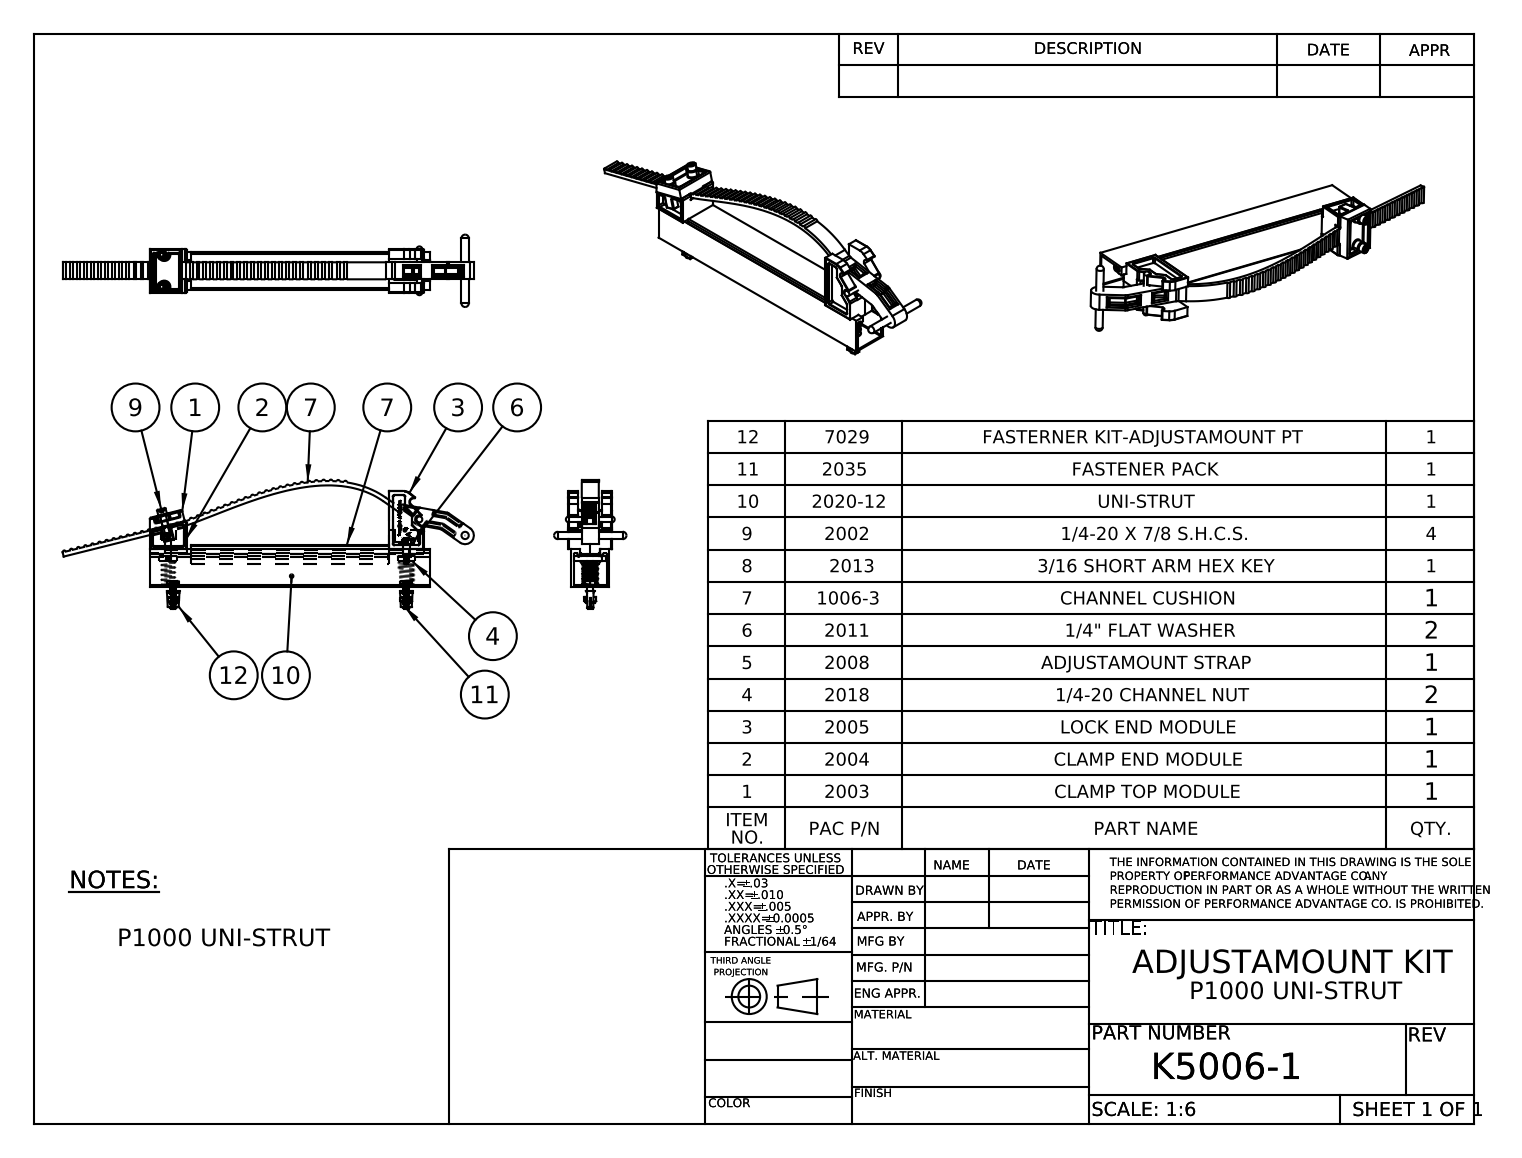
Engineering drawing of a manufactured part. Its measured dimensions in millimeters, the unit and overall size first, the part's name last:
Units: millimetres
Overall size (bounding box): 448.1 × 140.6 × 78.9
Round holes (diameter × count): ⌀5.1 ×6, ⌀6.4 ×2, ⌀6.8 ×2, ⌀7.3 ×2, ⌀8.4 ×2, ⌀6.6 ×1, ⌀7.4 ×1, ⌀15.9 ×1, ⌀16.3 ×1
Round bosses / shafts (diameter × count): ⌀6.4 ×7, ⌀9.5 ×4, ⌀15.9 ×2, ⌀10.3 ×2, ⌀9.5 ×2, ⌀4.7 ×2, ⌀8 ×1
Partial cylindrical surfaces — rounded edges, fillets, slot ends (radius × count): R1.6 ×66, R1.6 ×51, R0.8 ×43, R0.5 ×30, R1.5 ×8, R0.4 ×4, R6.4 ×4, R10.8 ×4
Main face-to-face distances: 41.3, 2.8, 38.5, 2, 35.7, 39.3, 4.8, 46.1, 44.1, 11.4
Hole centre spacings: 254, 259.4, 0.3, 5.4, 34.9
Volume: 393 900 mm³ · Surface area: 204 000 mm²
Bodies: 27 solids, 1587 faces (572 planar, 433 cylindrical, 582 other)
Part name (STEP PRODUCT): 7016; 7029; K5006-1; 2005 (+8 more)
STEP written by: SolidWorks 2014 (CONFIG_CONTROL_DESIGN)
